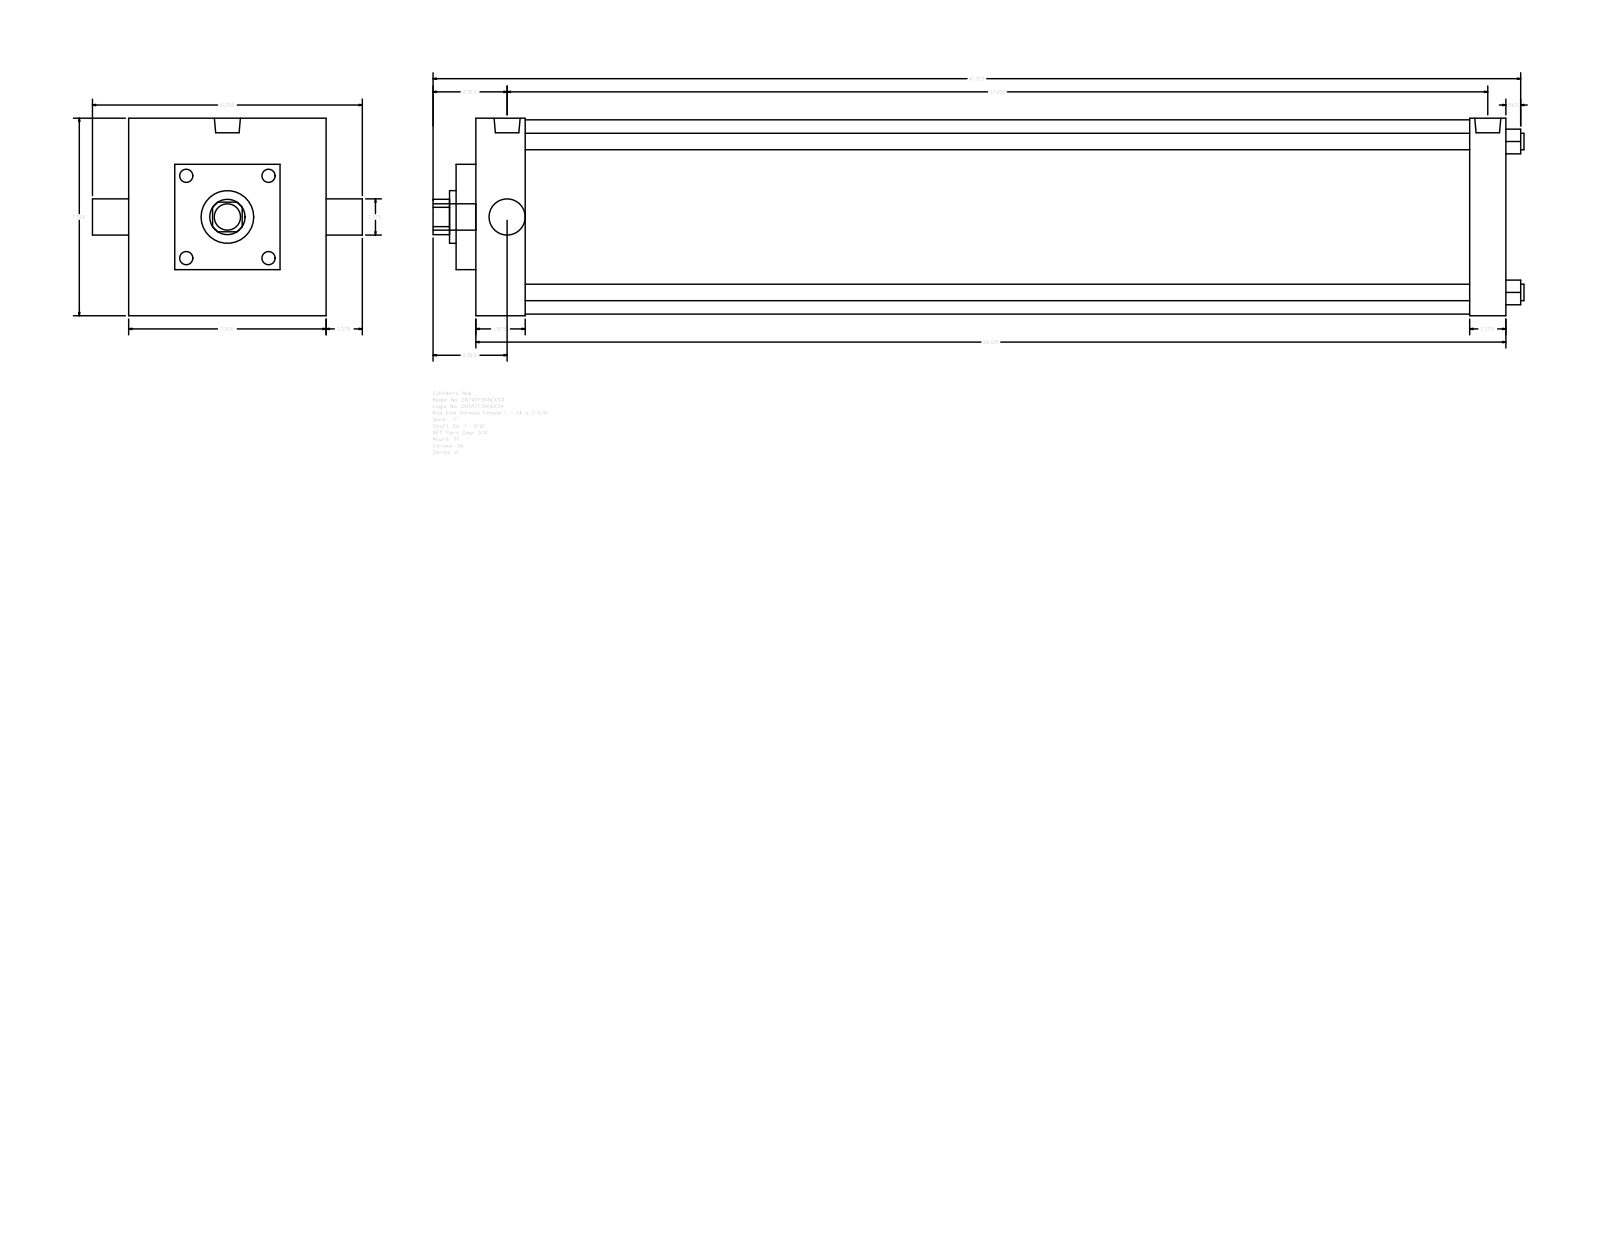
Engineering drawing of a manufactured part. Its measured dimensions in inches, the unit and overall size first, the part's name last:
Units: inches
Overall size (bounding box): 41.437 × 10.25 × 7.5
Round holes (diameter × count): ⌀0.625 ×4, ⌀1.375 ×2, ⌀2 ×1, ⌀7.375 ×1
Round bosses / shafts (diameter × count): ⌀0.594 ×3, ⌀0.989 ×2, ⌀1 ×1
Partial cylindrical surfaces — rounded edges, fillets, slot ends (radius × count): R0.672 ×1
Main face-to-face distances: 7.5, 39.125, 1.375, 0.75, 39.875, 2.625, 1.875, 37.25, 38.5, 37.75
Hole centre spacings: 4.052, 5.73, 8.103
Bodies: 0 solids, 89 faces (65 planar, 24 cylindrical, 0 other)
Part name (STEP PRODUCT): A_TF__0700_1.375
STEP written by: GSSL Pune (CONFIG_CONTROL_DESIGN)
